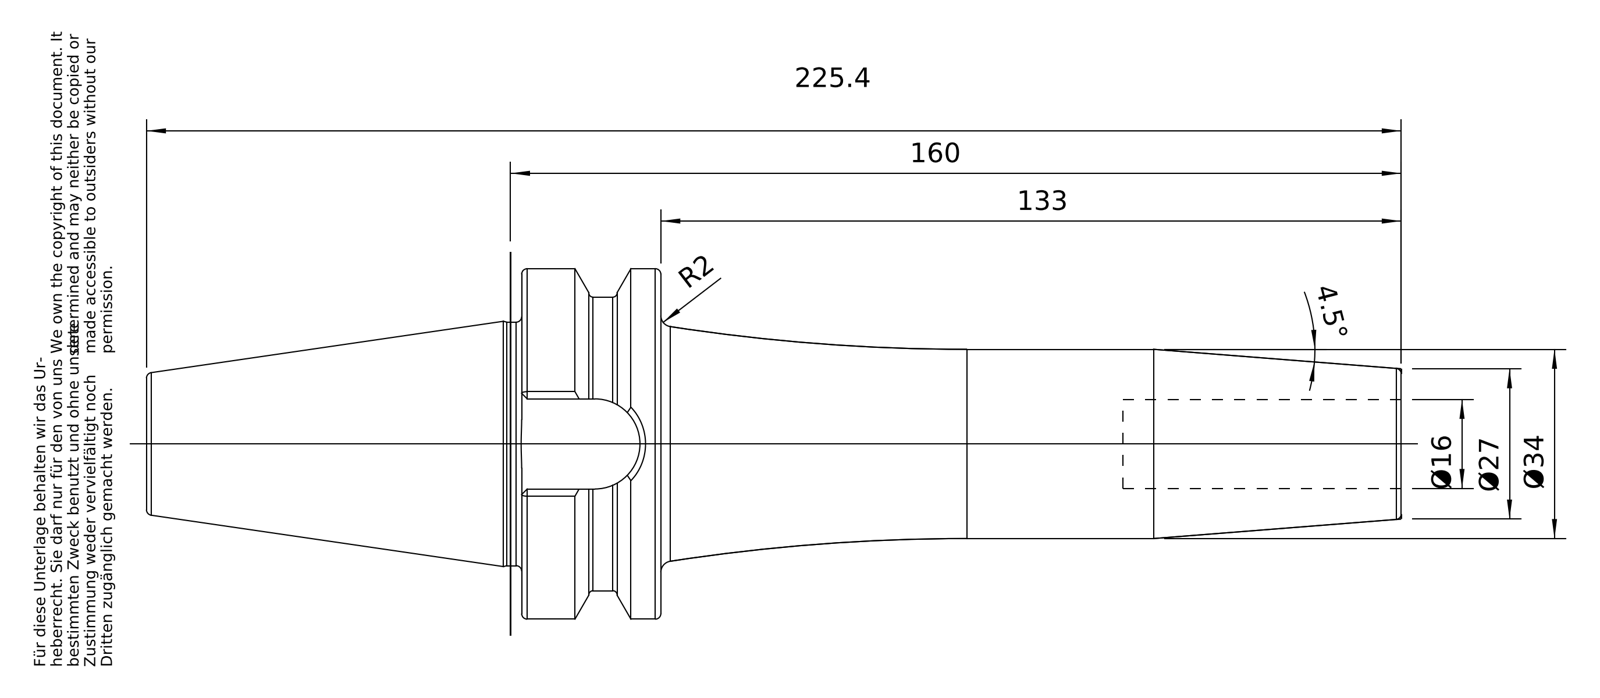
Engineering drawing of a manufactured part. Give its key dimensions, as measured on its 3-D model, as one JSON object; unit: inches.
{"part_name": "40-642-16", "step_written_by": "PRO/ENGINEER BY PARAMETRIC TECHNOLOGY CORPORATION, 2010430 (CONFIG_CONTROL_DESIGN)", "units": "inches", "bodies": {"solids": 1, "faces": 98, "planar": 26, "cylindrical": 22, "other": 50}, "overall_size": [8.874, 2.48, 2.48], "volume_in3": 14.54, "surface_area_in2": 58.34, "round_holes": [[0.545, 1], [0.63, 1], [0.67, 1], [0.689, 1]], "round_bosses_or_shafts": [[2.48, 1], [2.077, 1], [1.722, 1], [1.339, 1], [0.63, 1]], "partial_cylinders_radius": [[0.319, 1]], "face_to_face_distances": [0.984, 1.768, 6.22, 5.236, 4.252, 3.268, 1.969, 0.638, 2.654, 3.638]}
